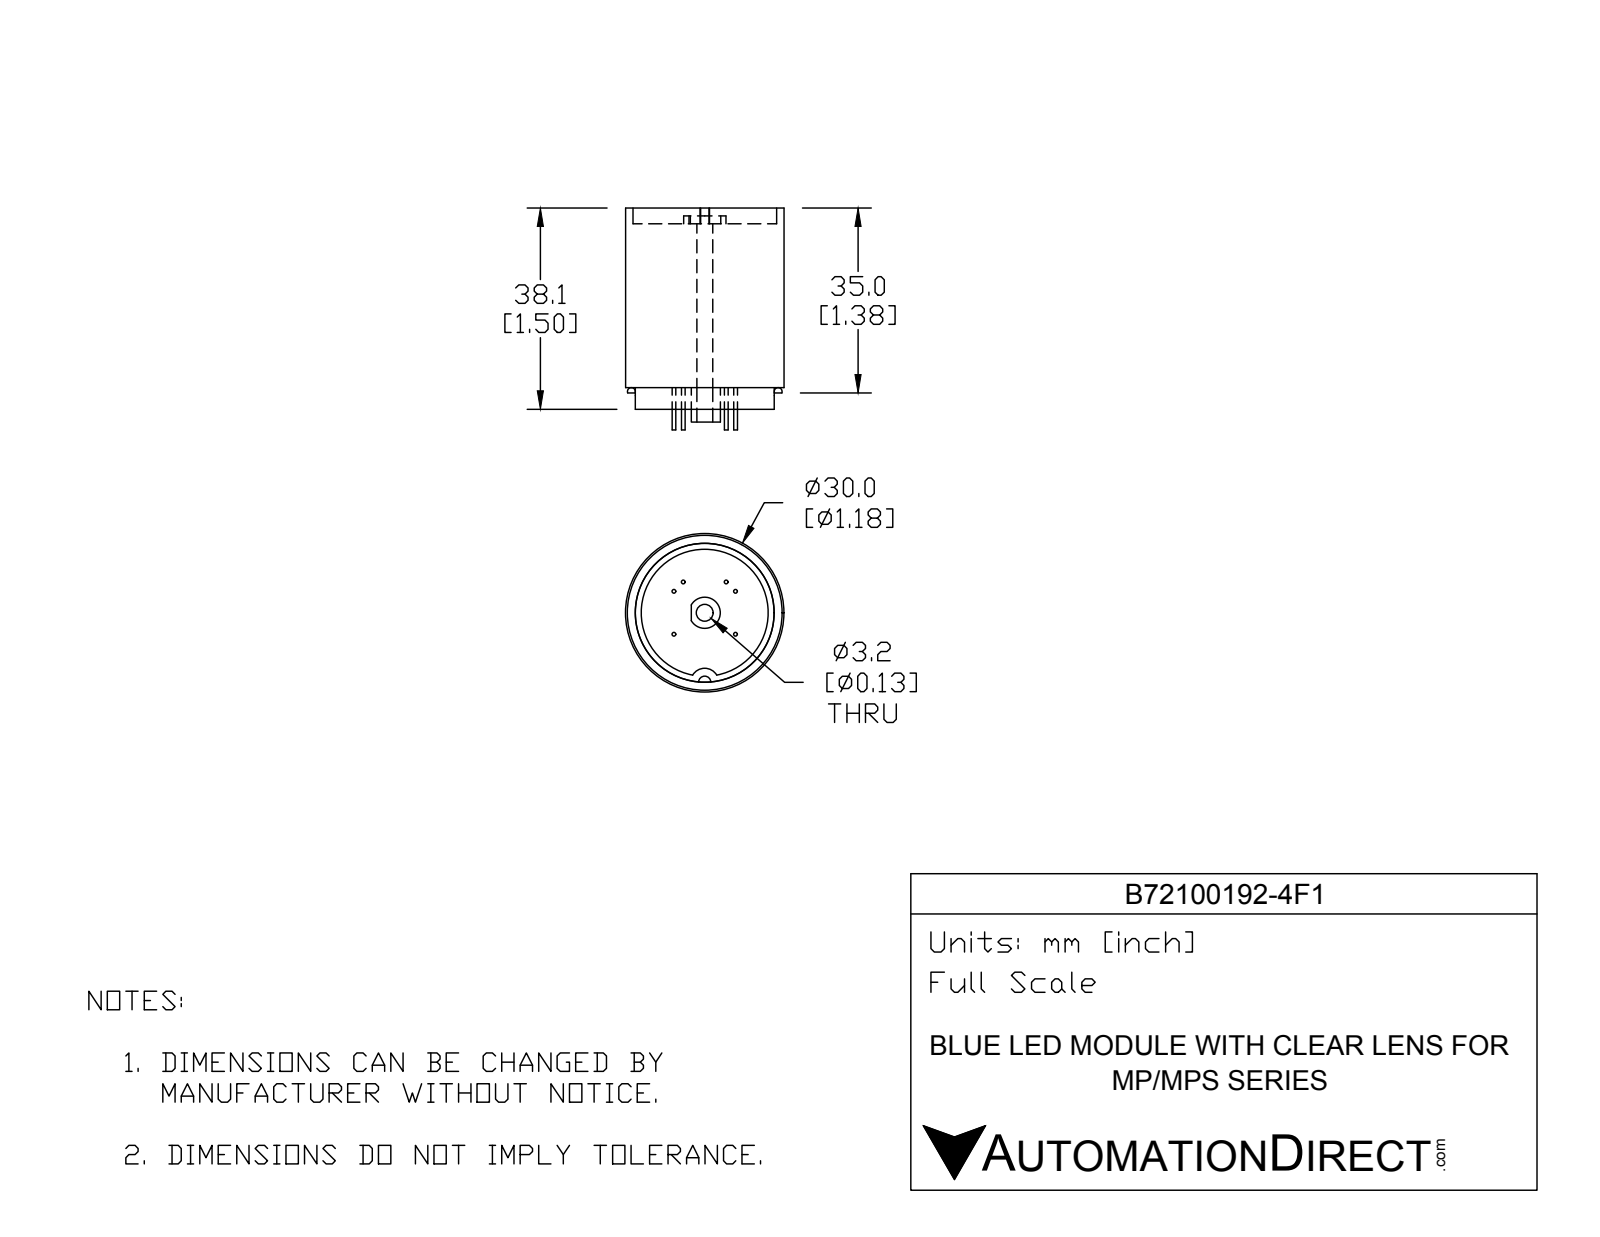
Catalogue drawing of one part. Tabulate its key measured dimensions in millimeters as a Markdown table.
| quantity | value |
| --- | --- |
| part name | B72100192-4F1 |
| STEP written by | SolidWorks 2016 (AUTOMOTIVE_DESIGN) |
| units | millimeters |
| bodies | 10 solids, 61 faces (25 planar, 32 cylindrical, 4 other) |
| overall size | 42 × 30 × 30 |
| volume | 22 770 mm³ |
| surface area | 6 653 mm² |
| round holes (diameter × count) | 3 × 1, 6.06 × 1, 24.04 × 1, 27.2 × 1 |
| round bosses / shafts (diameter × count) | 0.7 × 6, 30 × 1, 26.3 × 1, 8 × 1, 5.9 × 1 |
| main face-to-face distances | 31, 34, 3, 4.1, 35.1, 38.1, 1.5, 36.6, 32.5, 2.42 |
